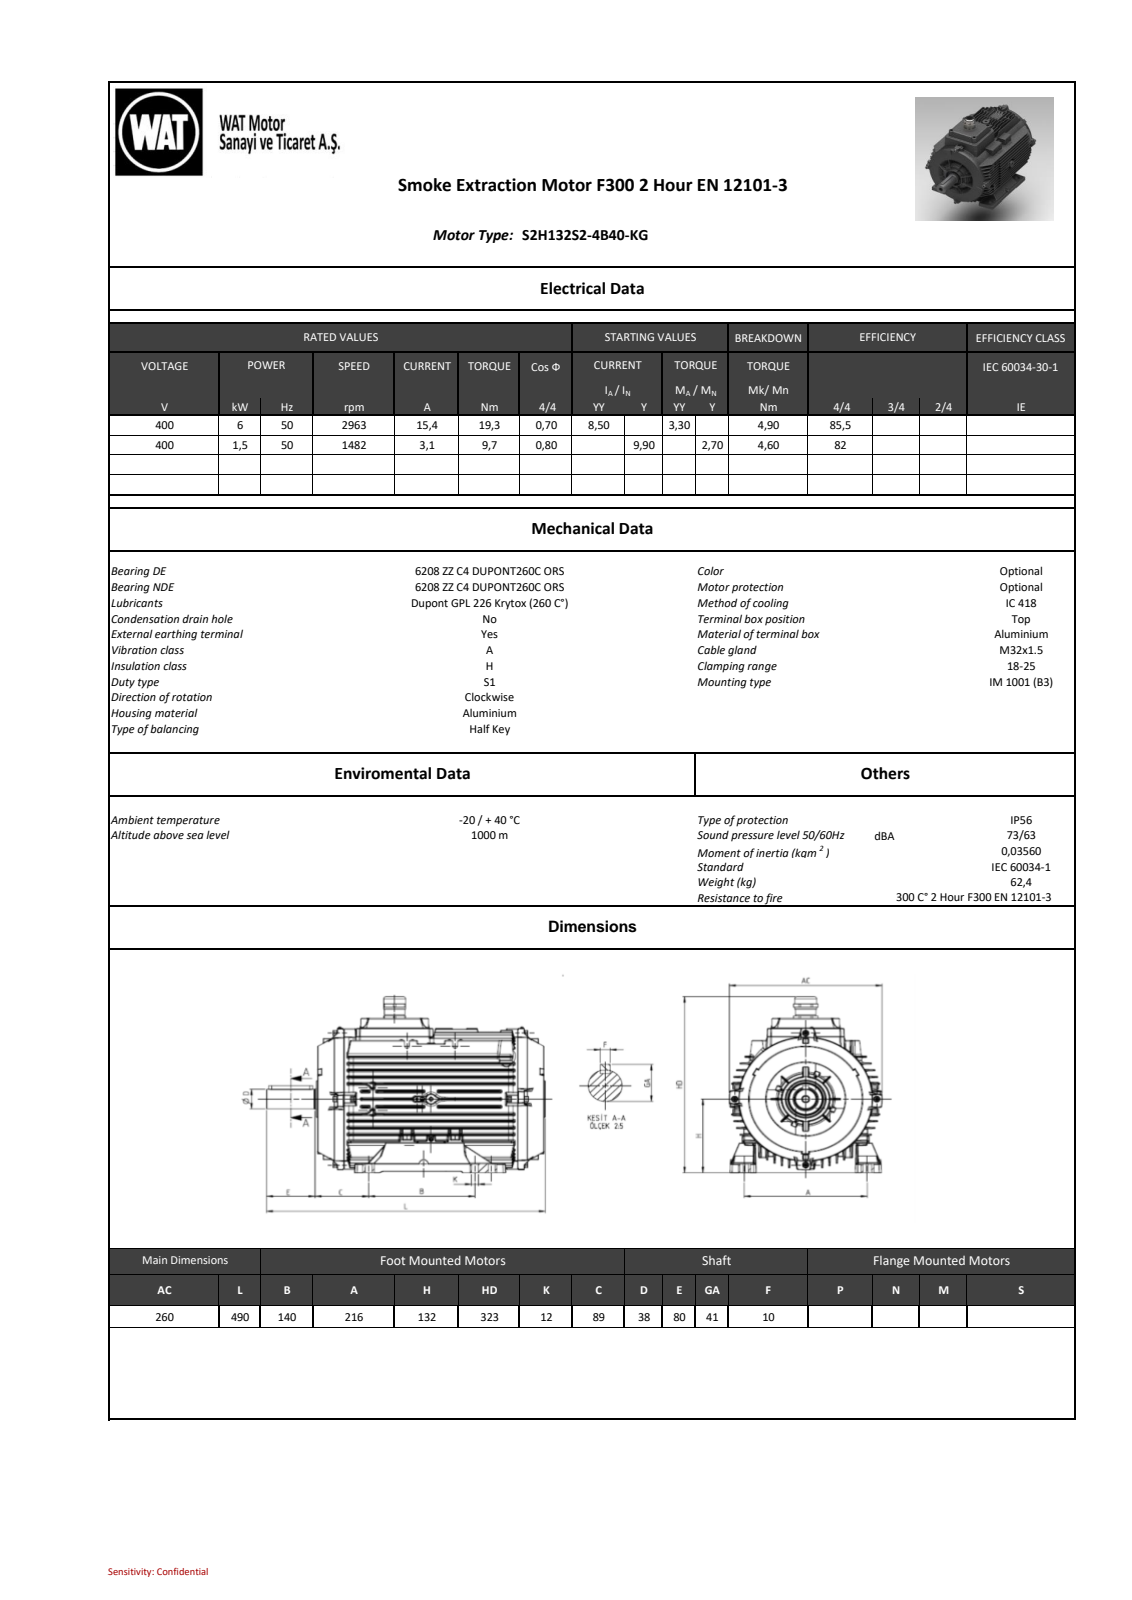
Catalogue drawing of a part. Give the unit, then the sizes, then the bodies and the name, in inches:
Units: inches
Overall size (bounding box): 19.272 × 12.724 × 10.236
Round holes (diameter × count): ⌀0.165 ×3, ⌀0.268 ×2, ⌀0.315 ×2, ⌀0.413 ×1, ⌀0.709 ×1, ⌀1.732 ×1, ⌀2.299 ×1, ⌀2.307 ×1
Round bosses / shafts (diameter × count): ⌀0.583 ×4, ⌀0.512 ×4, ⌀0.394 ×4, ⌀9.075 ×1, ⌀1.575 ×1, ⌀1.496 ×1, ⌀1.472 ×1, ⌀1.165 ×1
Partial cylindrical surfaces — rounded edges, fillets, slot ends (radius × count): R0.031 ×1047, R0.039 ×696, R0.059 ×111, R0.02 ×70, R0.079 ×68, R0.118 ×22, R0.197 ×12, R0.004 ×10
Main face-to-face distances: 0.41, 0.416, 0.82, 0.405, 4.944, 3.309, 4.535, 4.13, 3.719, 0.409
Hole centre spacings: 1.26, 10.295
Bodies: 0 solids, 8089 faces (1705 planar, 2802 cylindrical, 3582 other)
Part name (STEP PRODUCT): 260314206C66ee8s
STEP written by: SIEMENS PLM Software NX 11.0 (AP203_CONFIGURATION_CONTROLLED_3D_DESIGN_OF_MECHANICAL_PARTS_AND_ASSEMBLIES_MIM_LF)
